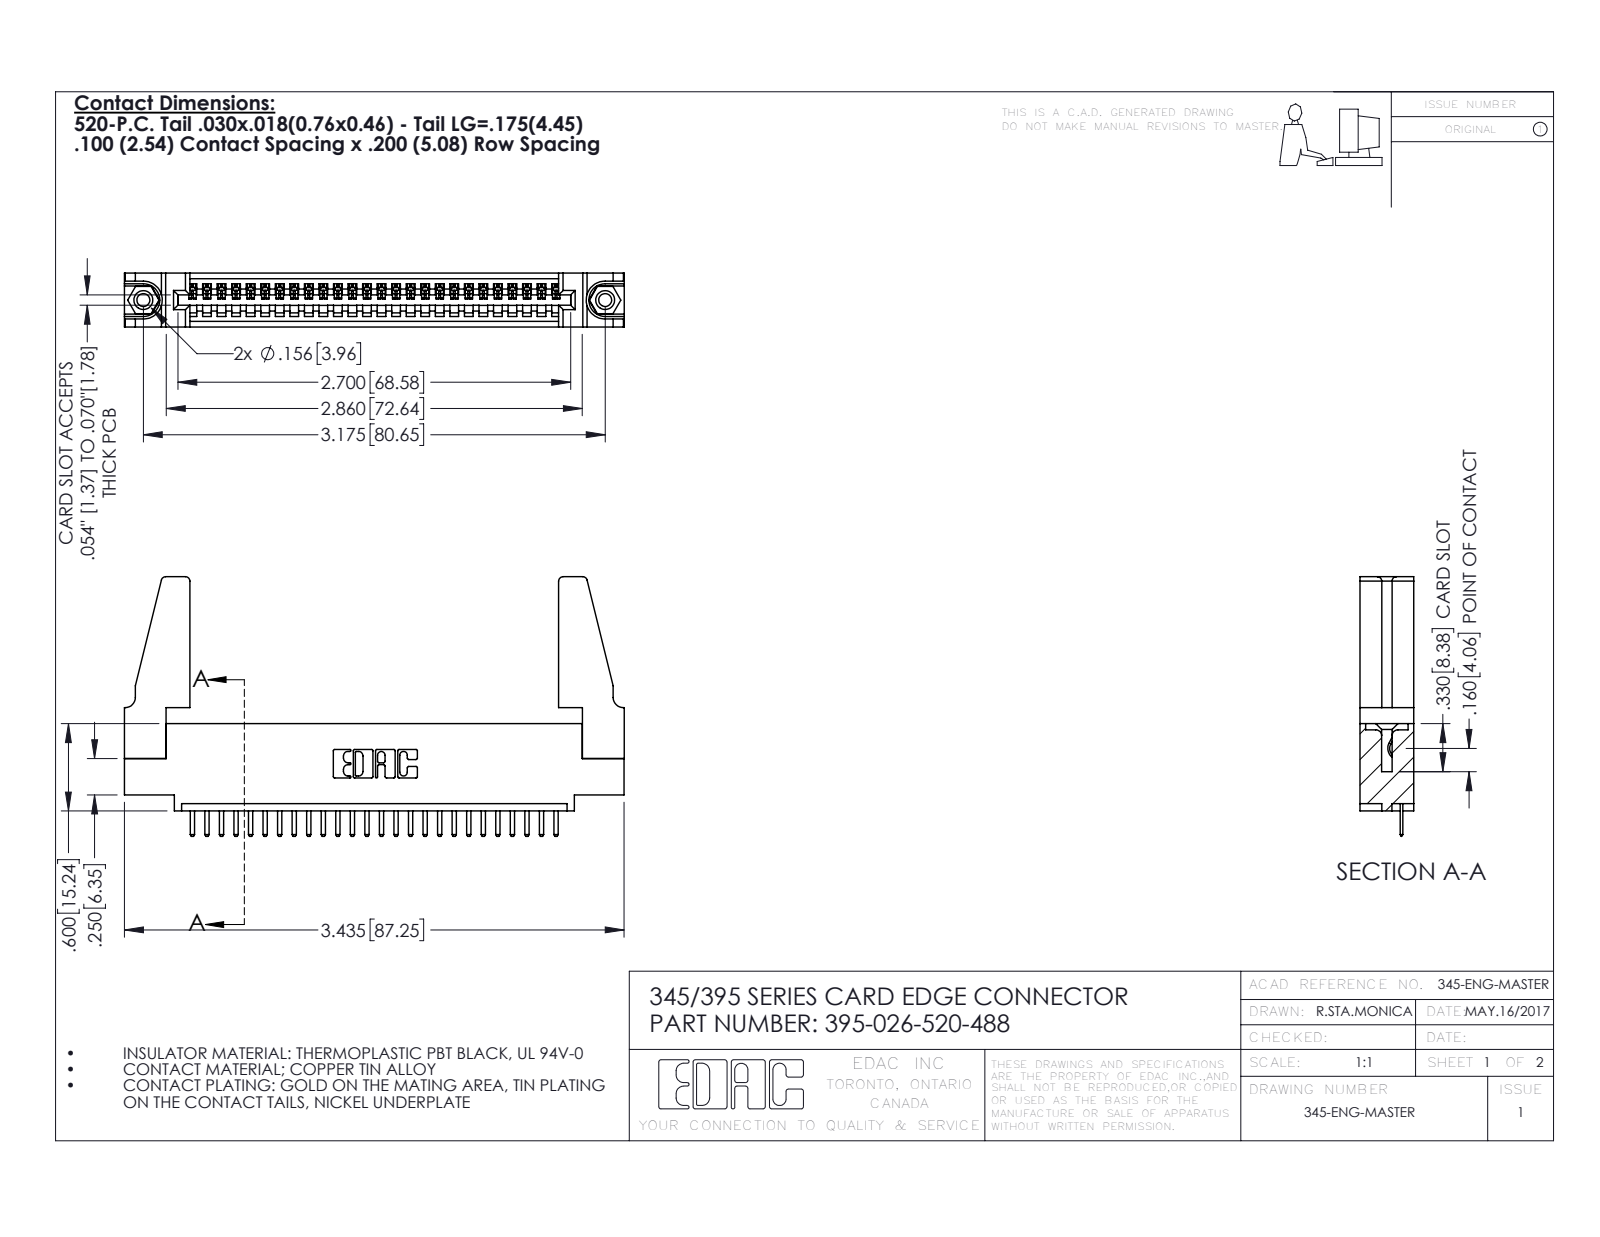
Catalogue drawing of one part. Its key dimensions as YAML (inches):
part_name: "345-292-001_345-293-120; 395-026-520-488; 345 Part_0.110 Offset - 0.156 Dia-TH; 345-220-078_345-220-088 (+1 more)"
step_written_by: "SolidWorks 2016 (CONFIG_CONTROL_DESIGN)"
units: inches
bodies: {solids: 31, faces: 1866, planar: 1248, cylindrical: 602, other: 16}
overall_size: [3.436, 1.785, 0.37]
volume: 0.687
surface_area: 20.76
round_holes:
  - {diameter: 0.089, count: 2}
  - {diameter: 0.125, count: 2}
  - {diameter: 0.156, count: 2}
  - {diameter: 0.064, count: 1}
round_bosses_or_shafts:
  - {diameter: 0.155, count: 2}
partial_cylinders:
  - {radius: 0.01, count: 54}
  - {radius: 0.006, count: 52}
  - {radius: 0.01, count: 22}
  - {radius: 0.03, count: 8}
  - {radius: 0.007, count: 6}
  - {radius: 0.031, count: 6}
  - {radius: 0.026, count: 3}
  - {radius: 0.031, count: 2}
face_to_face_distances: [0.37, 0.072, 0.298, 0.2, 0.098, 0.272, 0.025, 0.225, 0.072, 0.149]
hole_center_spacings: [0.27, 2.94, 3.175]
